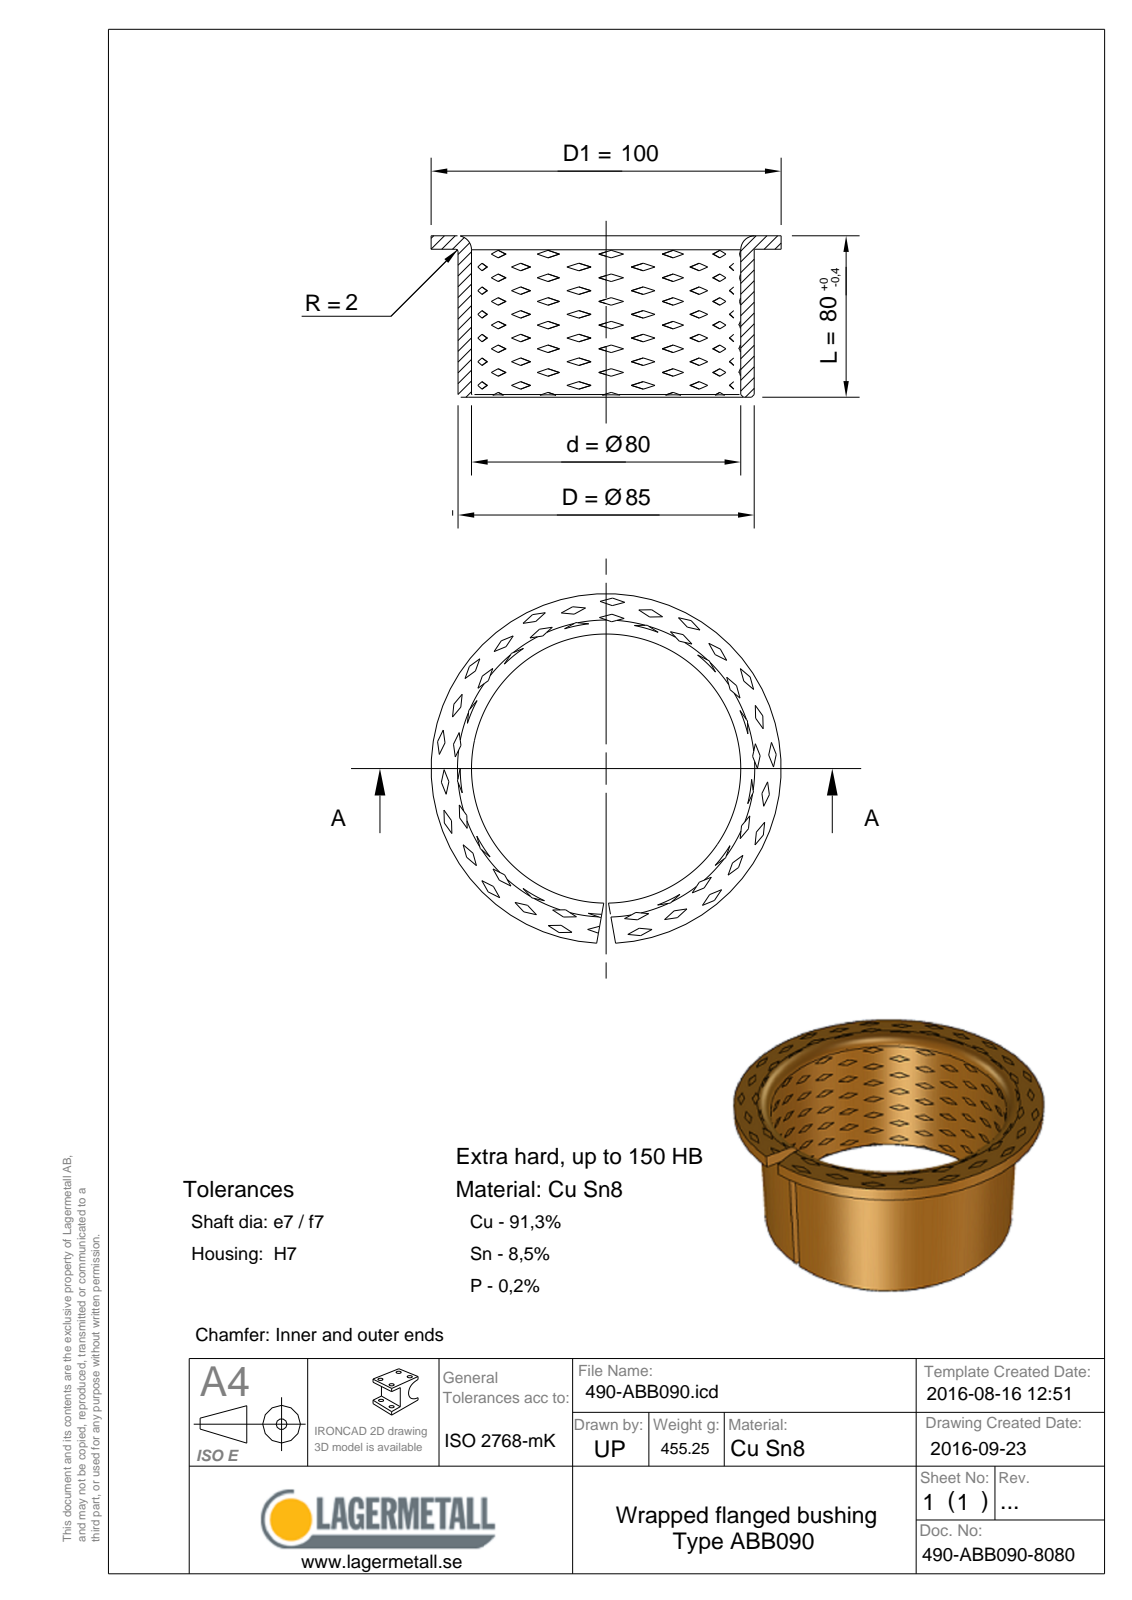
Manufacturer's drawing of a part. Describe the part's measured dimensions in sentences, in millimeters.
Its 3-D file was written by "Spatial InterOp 3D (CONFIG_CONTROL_DESIGN)". It is 1 solid with 25 faces: 5 planar, 8 cylindrical and 12 other. Overall it measures 100 by 100 by 80 millimeters. Its volume is 56 203 cubic millimeters and its surface area 46 710 square millimeters. Round holes: 1 of diameter 80. Round bosses or shafts: 1 of diameter 100, 1 of diameter 85. The main face-to-face distances are 2.5, 77.5, 80.
